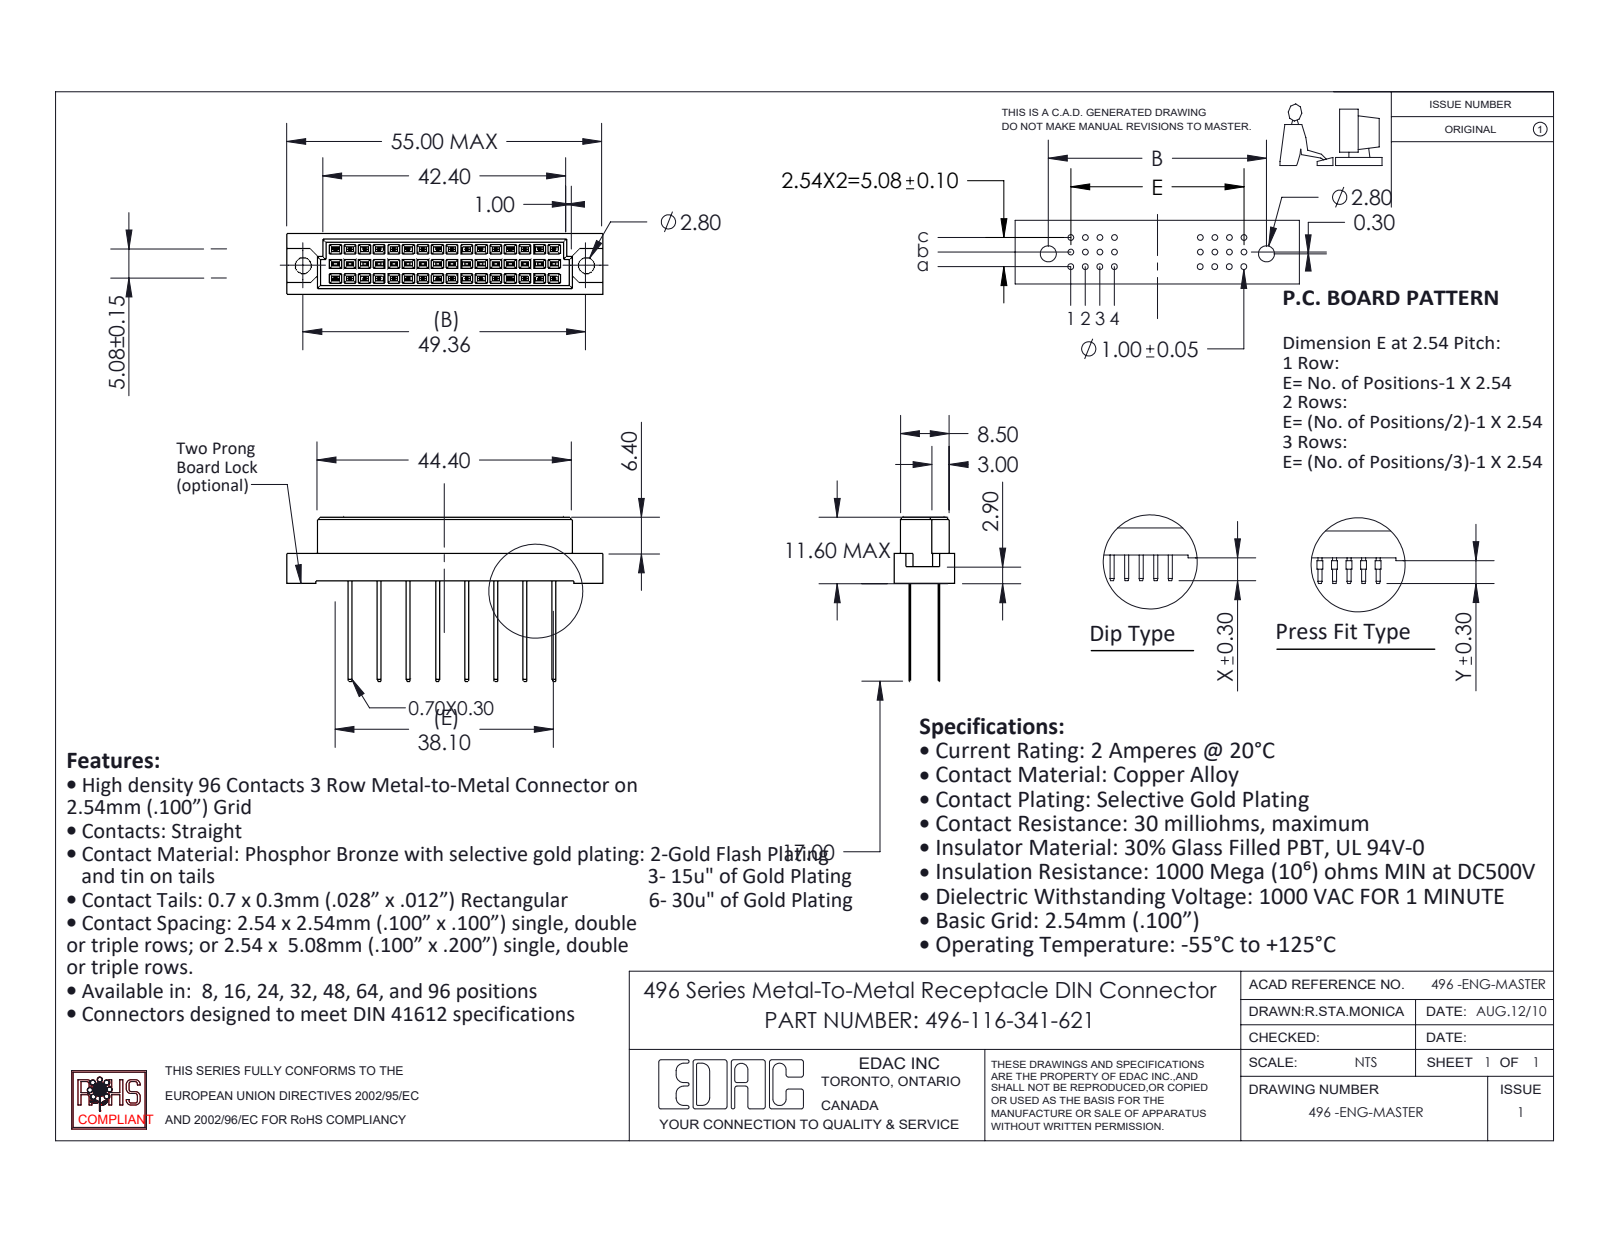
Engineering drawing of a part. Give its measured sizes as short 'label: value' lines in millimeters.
name: 496 Part_48; 496-116-341-621; 496-290_41
written by: SolidWorks 2020 (CONFIG_CONTROL_DESIGN)
unit: mm
bodies: 17 solids, 826 faces (822 planar, 4 cylindrical, 0 other)
size: 55 × 28.6 × 10.6
volume: 4 661 mm³; area: 4 903 mm²
holes: 2× ⌀2.8
face distances: 5.08, 2.54, 1.05, 9.55, 0.81, 2.61, 2.91, 7.69, 7.99, 1.56
hole spacings: 49.36
